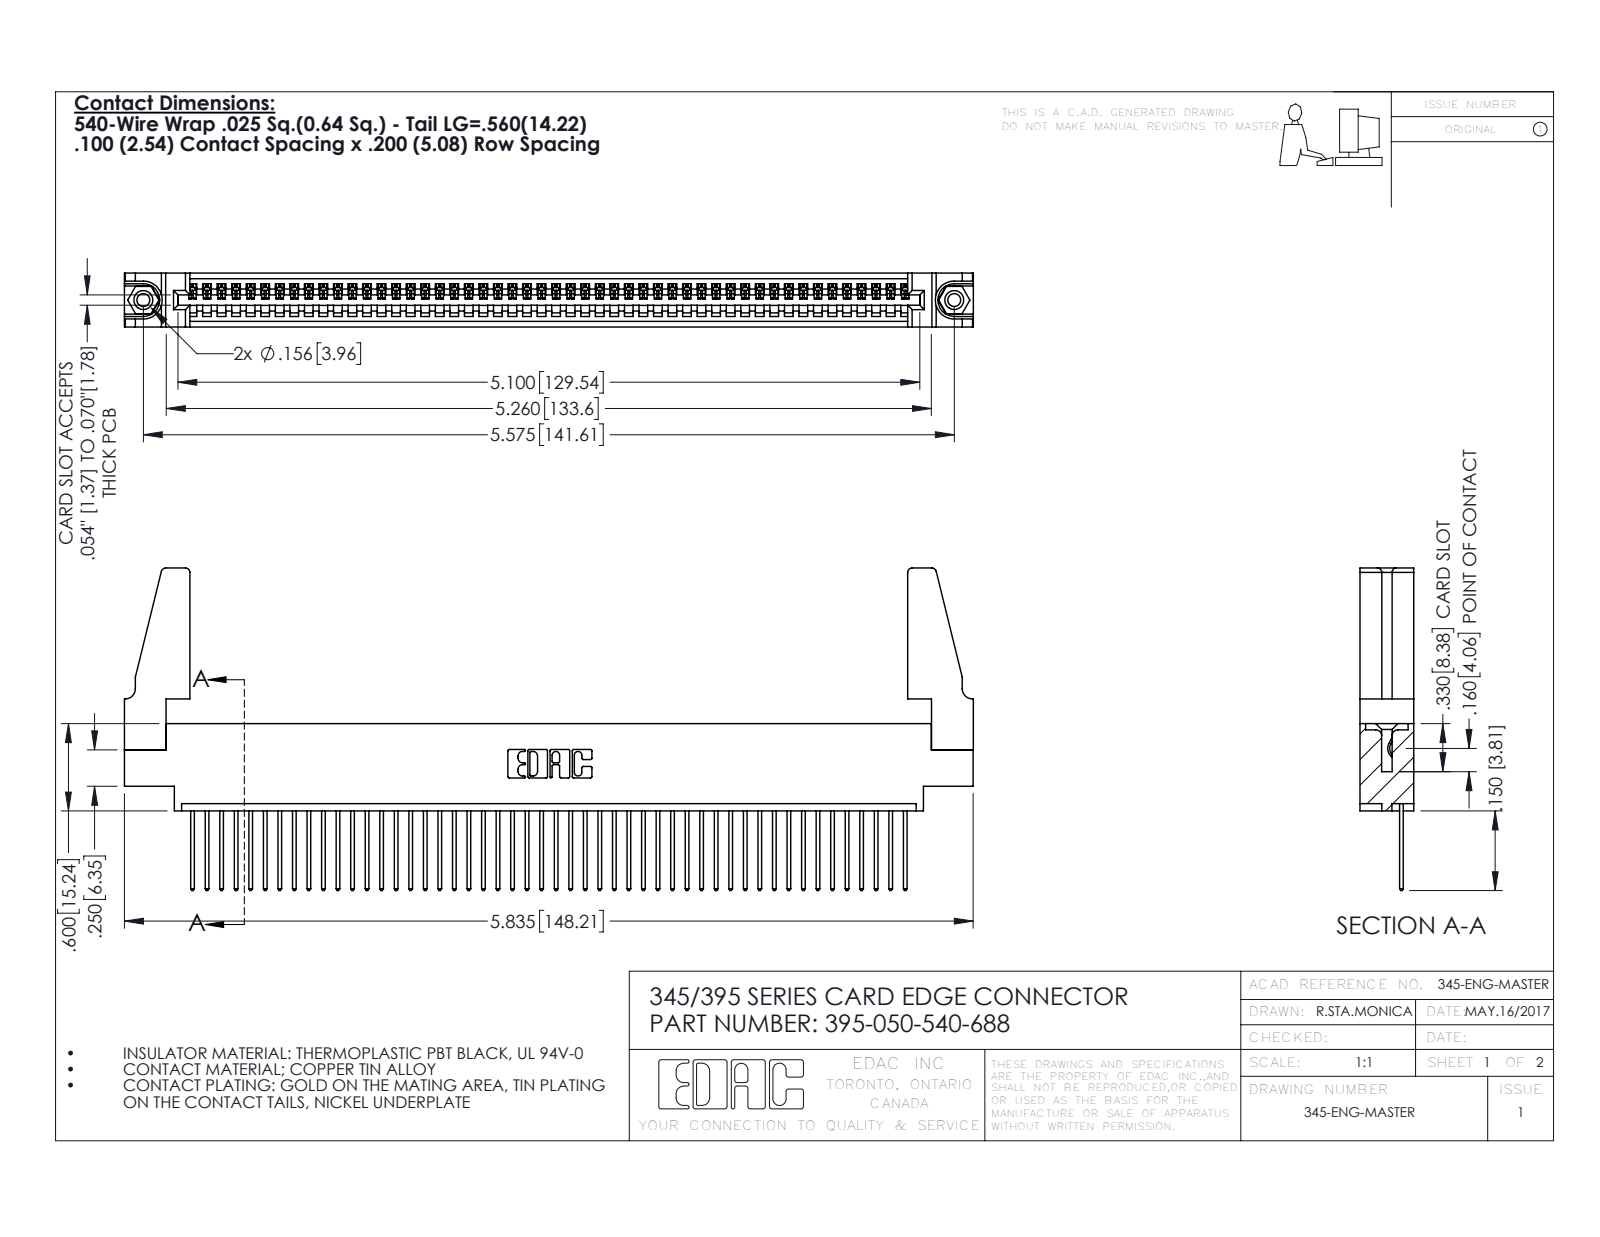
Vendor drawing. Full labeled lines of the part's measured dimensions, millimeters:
Part name (STEP PRODUCT): 345-250-001_345-250-001-102; 345-220-078_345-220-088; 345-292-001_345-293-140; 395-050-540-688 (+1 more)
STEP written by: SolidWorks 2016 (CONFIG_CONTROL_DESIGN)
Units: millimetres
Bodies: 55 solids, 3154 faces (2156 planar, 982 cylindrical, 16 other)
Overall size (bounding box): 148.2 × 56.3 × 9.4
Volume: 17 350 mm³ · Surface area: 22 590 mm²
Round holes (diameter × count): ⌀2.3 ×2, ⌀3.2 ×2, ⌀4 ×2, ⌀1.6 ×1
Round bosses / shafts (diameter × count): ⌀3.9 ×2
Partial cylindrical surfaces — rounded edges, fillets, slot ends (radius × count): R0.2 ×100, R0.3 ×100, R0.3 ×22, R0.8 ×8, R0.2 ×6, R0.8 ×6, R0.7 ×3, R0.8 ×2
Main face-to-face distances: 1.8, 7.6, 9.4, 2.5, 6.9, 0.6, 5.1, 5.7, 4.4, 3.8
Hole centre spacings: 6.9, 135.6, 141.6
